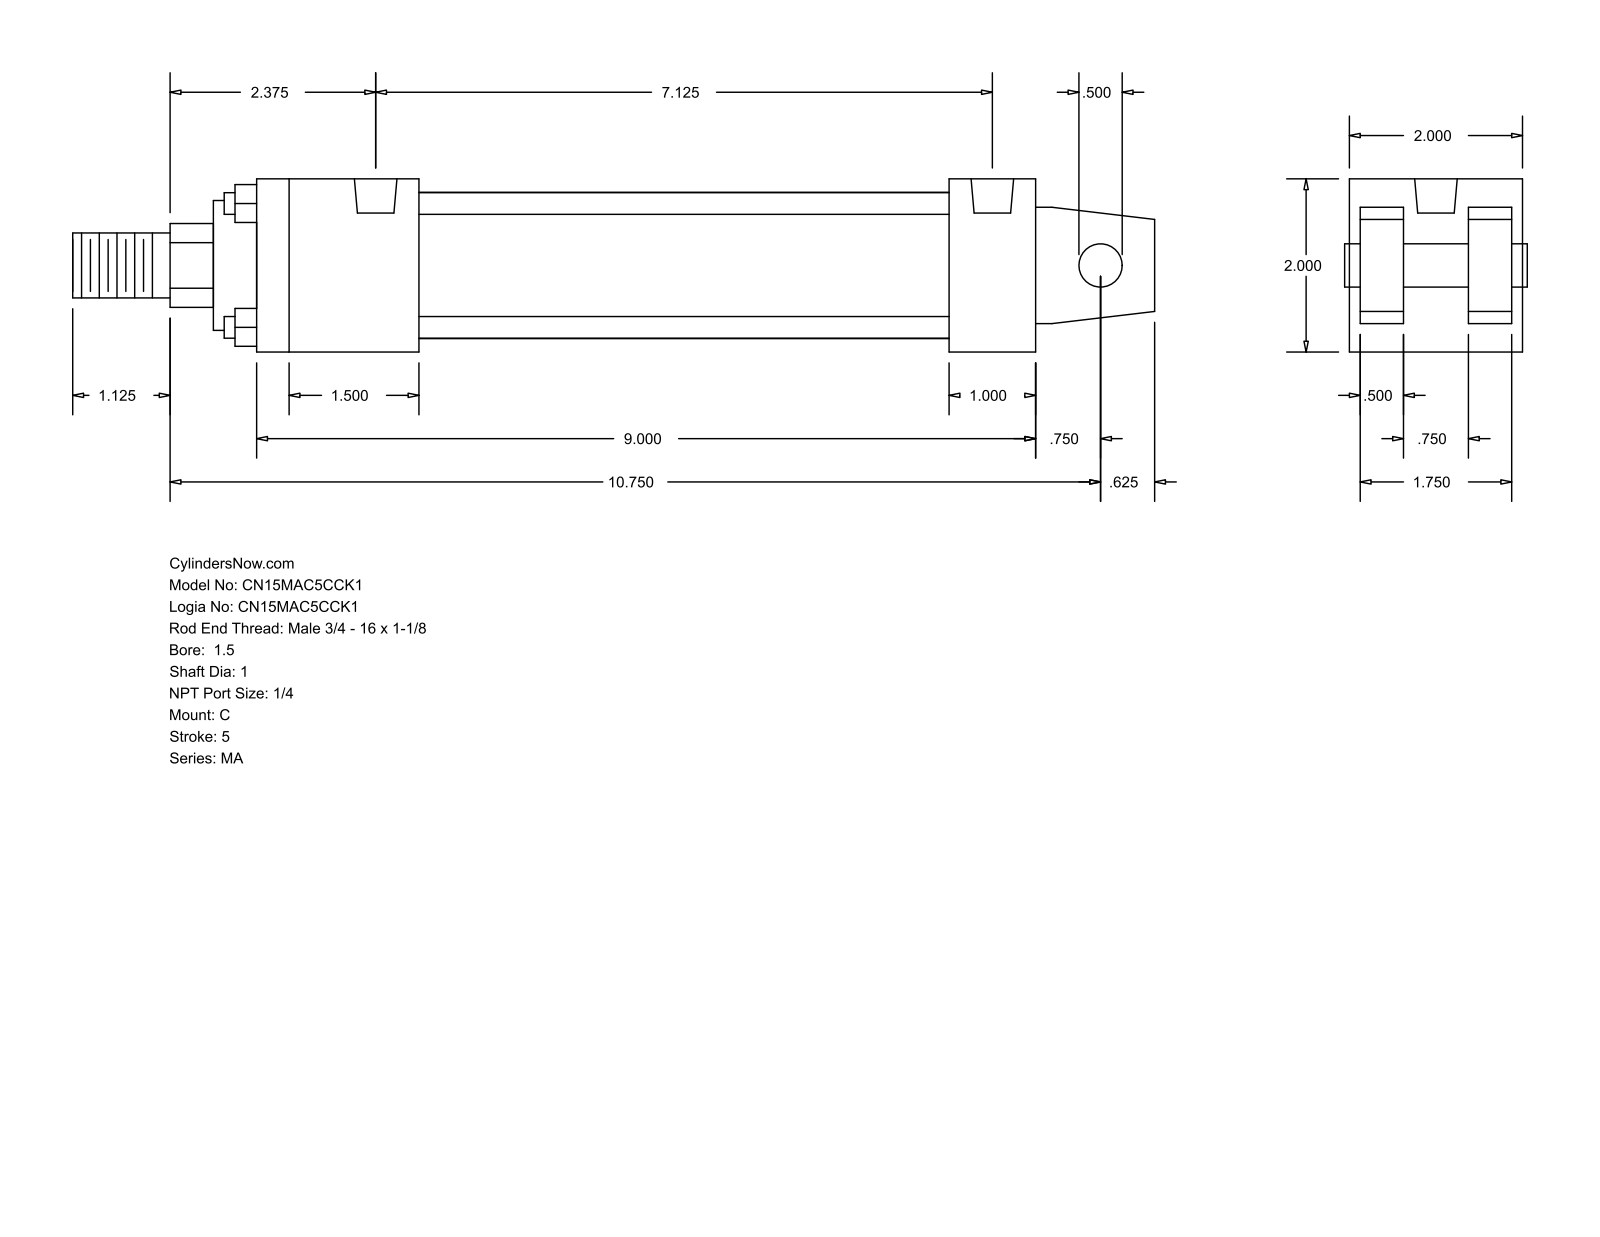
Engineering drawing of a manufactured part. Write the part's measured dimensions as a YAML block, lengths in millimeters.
part_name: "MA_C__0150_1"
step_written_by: "GSSL Pune (CONFIG_CONTROL_DESIGN)"
units: millimeters
bodies: {solids: 0, faces: 103, planar: 76, cylindrical: 27, other: 0}
overall_size: [317.5, 50.8, 50.8]
round_holes:
  - {diameter: 7.94, count: 4}
  - {diameter: 12.49, count: 2}
round_bosses_or_shafts:
  - {diameter: 6.35, count: 4}
  - {diameter: 42.93, count: 1}
  - {diameter: 38.1, count: 1}
  - {diameter: 25.4, count: 1}
  - {diameter: 19.05, count: 1}
  - {diameter: 12.7, count: 1}
partial_cylinders:
  - {radius: 12.29, count: 1}
face_to_face_distances: [50.8, 47.63, 12.7, 34.93, 3.17, 15.87, 31.76, 60.33, 215.9, 228.6]
hole_center_spacings: [180.97]
